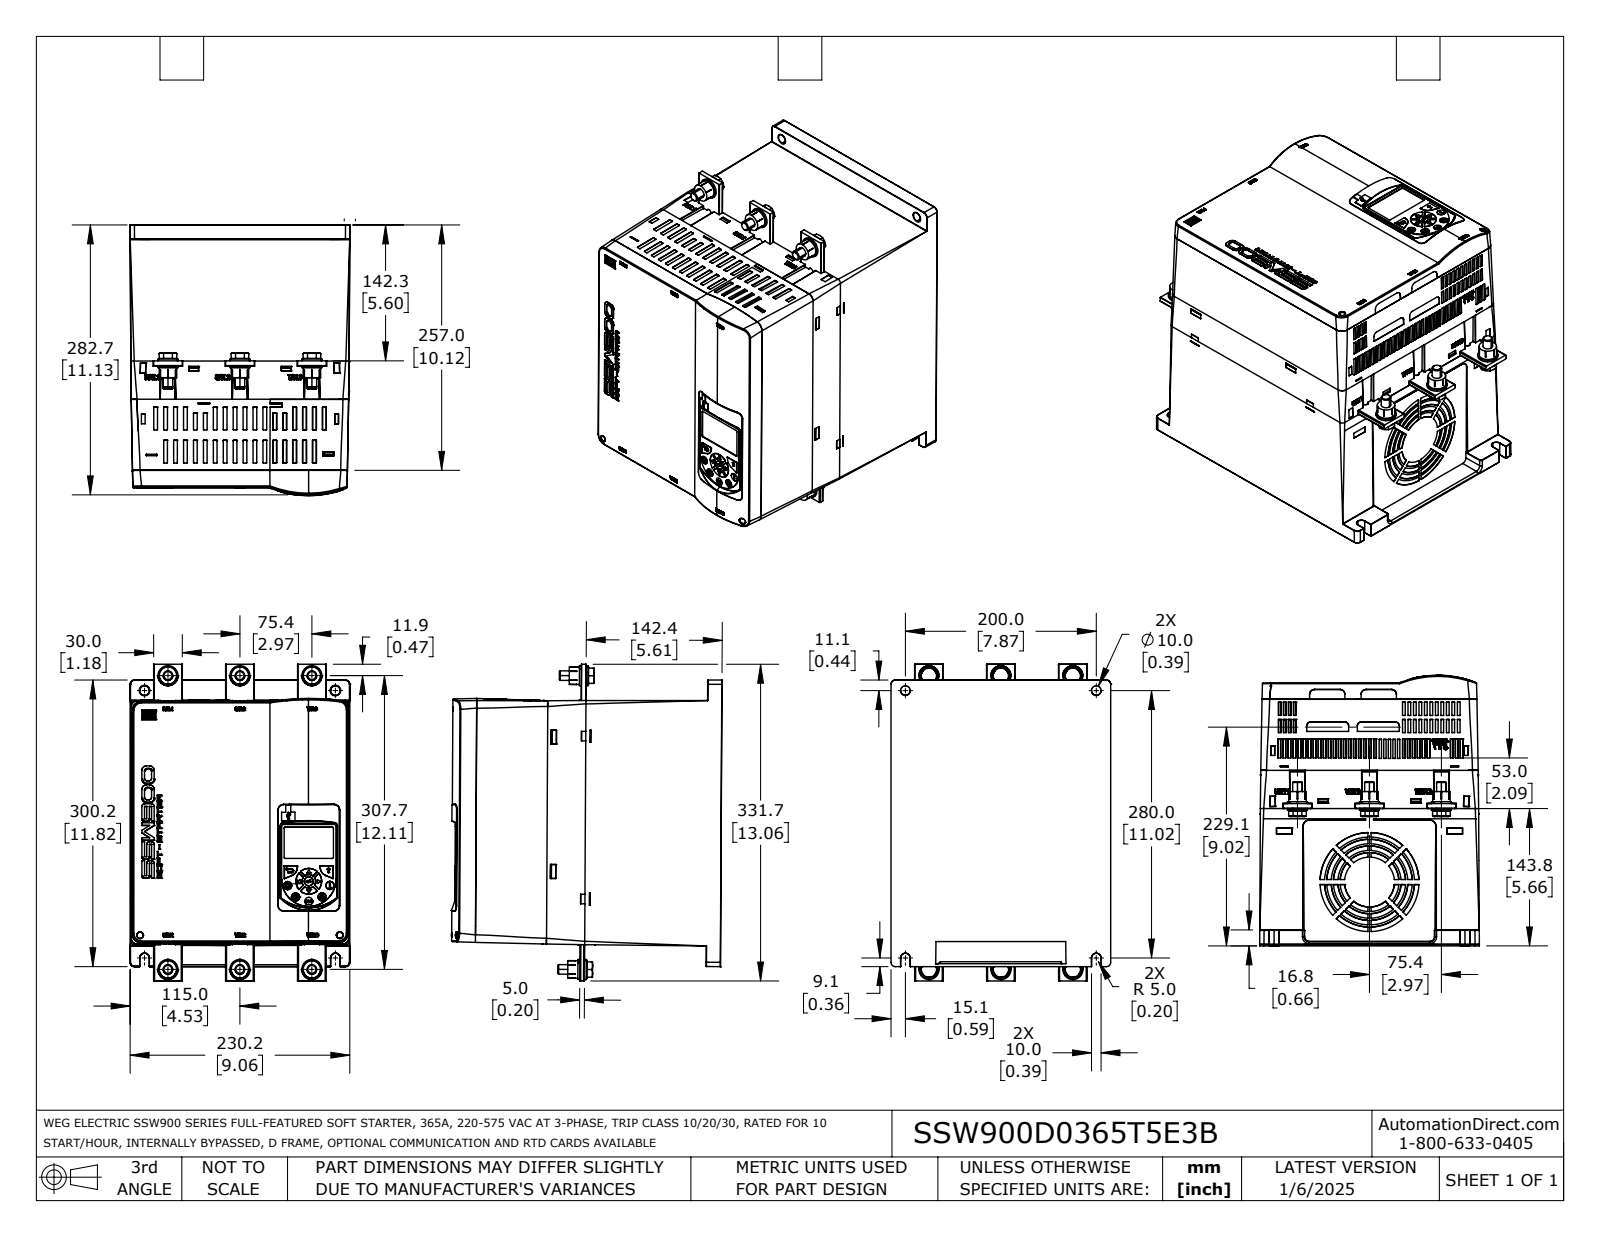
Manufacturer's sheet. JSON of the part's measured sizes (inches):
{"part_name": "SSW900D0365T5E3B", "step_written_by": "SolidWorks 2021 (AUTOMOTIVE_DESIGN)", "units": "inches", "bodies": {"solids": 1, "faces": 4211, "planar": 2804, "cylindrical": 500, "other": 907}, "overall_size": [13.059, 11.161, 9.061], "volume_in3": 173.2, "surface_area_in2": 1261, "round_holes": [[0.395, 2], [0.133, 1], [0.261, 1], [2.43, 1], [2.981, 1], [3.533, 1], [4.084, 1]], "round_bosses_or_shafts": [[0.827, 9], [0.72, 6], [0.394, 6], [3.712, 1], [3.16, 1], [2.609, 1], [0.151, 1], [0.057, 1]], "partial_cylinders_radius": [[0.012, 103], [0.018, 24], [0.017, 22], [0.018, 22], [0.019, 20], [0.039, 17], [0.006, 7], [0.079, 6]], "face_to_face_distances": [0.705, 9.78, 10.796, 10.091, 0.098, 0.679, 10.117, 9.412, 0.581, 10.698], "hole_center_spacings": [7.874, 10.141, 12.95]}
